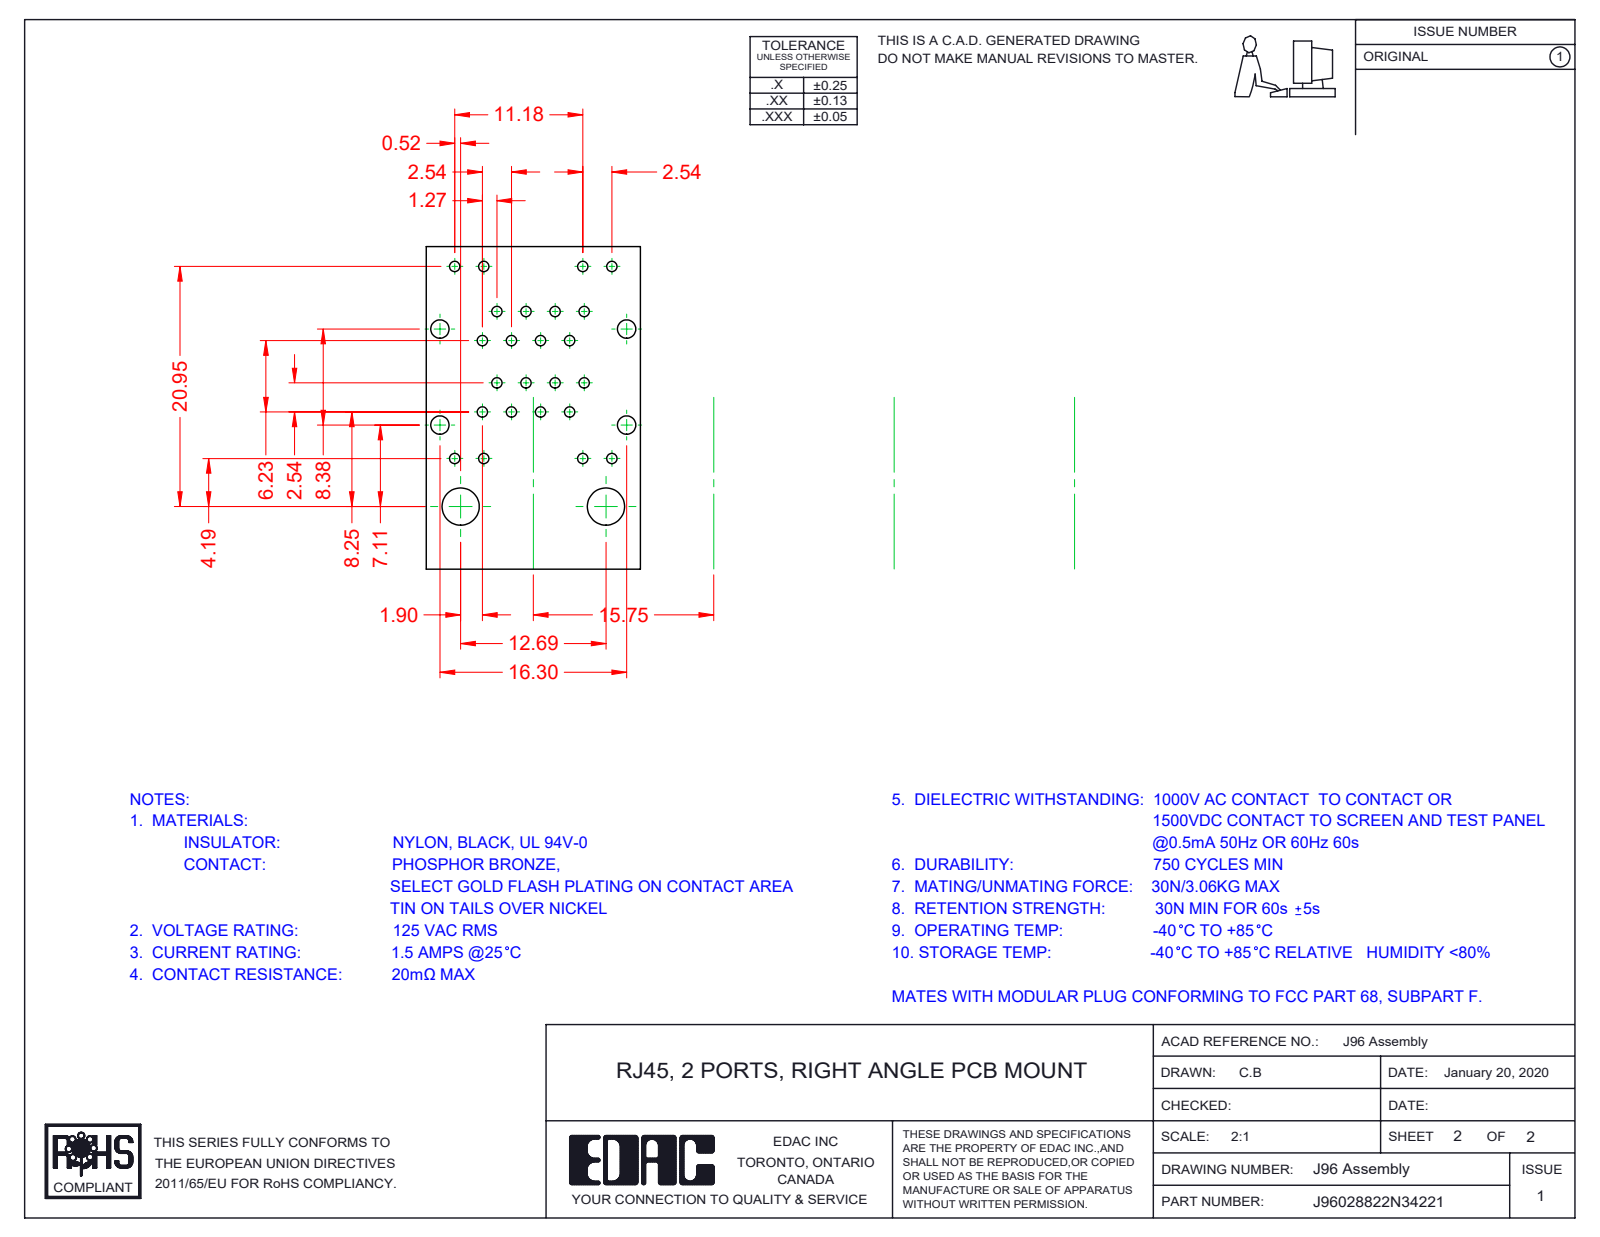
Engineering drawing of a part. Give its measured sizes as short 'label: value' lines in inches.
name: 96 Back Plate_2 Ports; J96028822N34221; 96 Shield_2 Ports LED - EMI; 96 Contact Lock Upper (+8 more)
written by: SolidWorks 2016 (CONFIG_CONTROL_DESIGN)
unit: in
bodies: 27 solids, 2417 faces (1865 planar, 446 cylindrical, 106 other)
size: 1.235 × 1.129 × 0.661
volume: 0.418 in³; area: 29.6 in²
rounds: 48× R0.01, 32× R0.006, 24× R0.014, 16× R0.02, 16× R0.039, 14× R0.008, 9× R0.028, 5× R0.079
face distances: 0.642, 0.634, 0.069, 0.65, 0.581, 0.061, 0.573, 0.021, 0.058, 0.441
